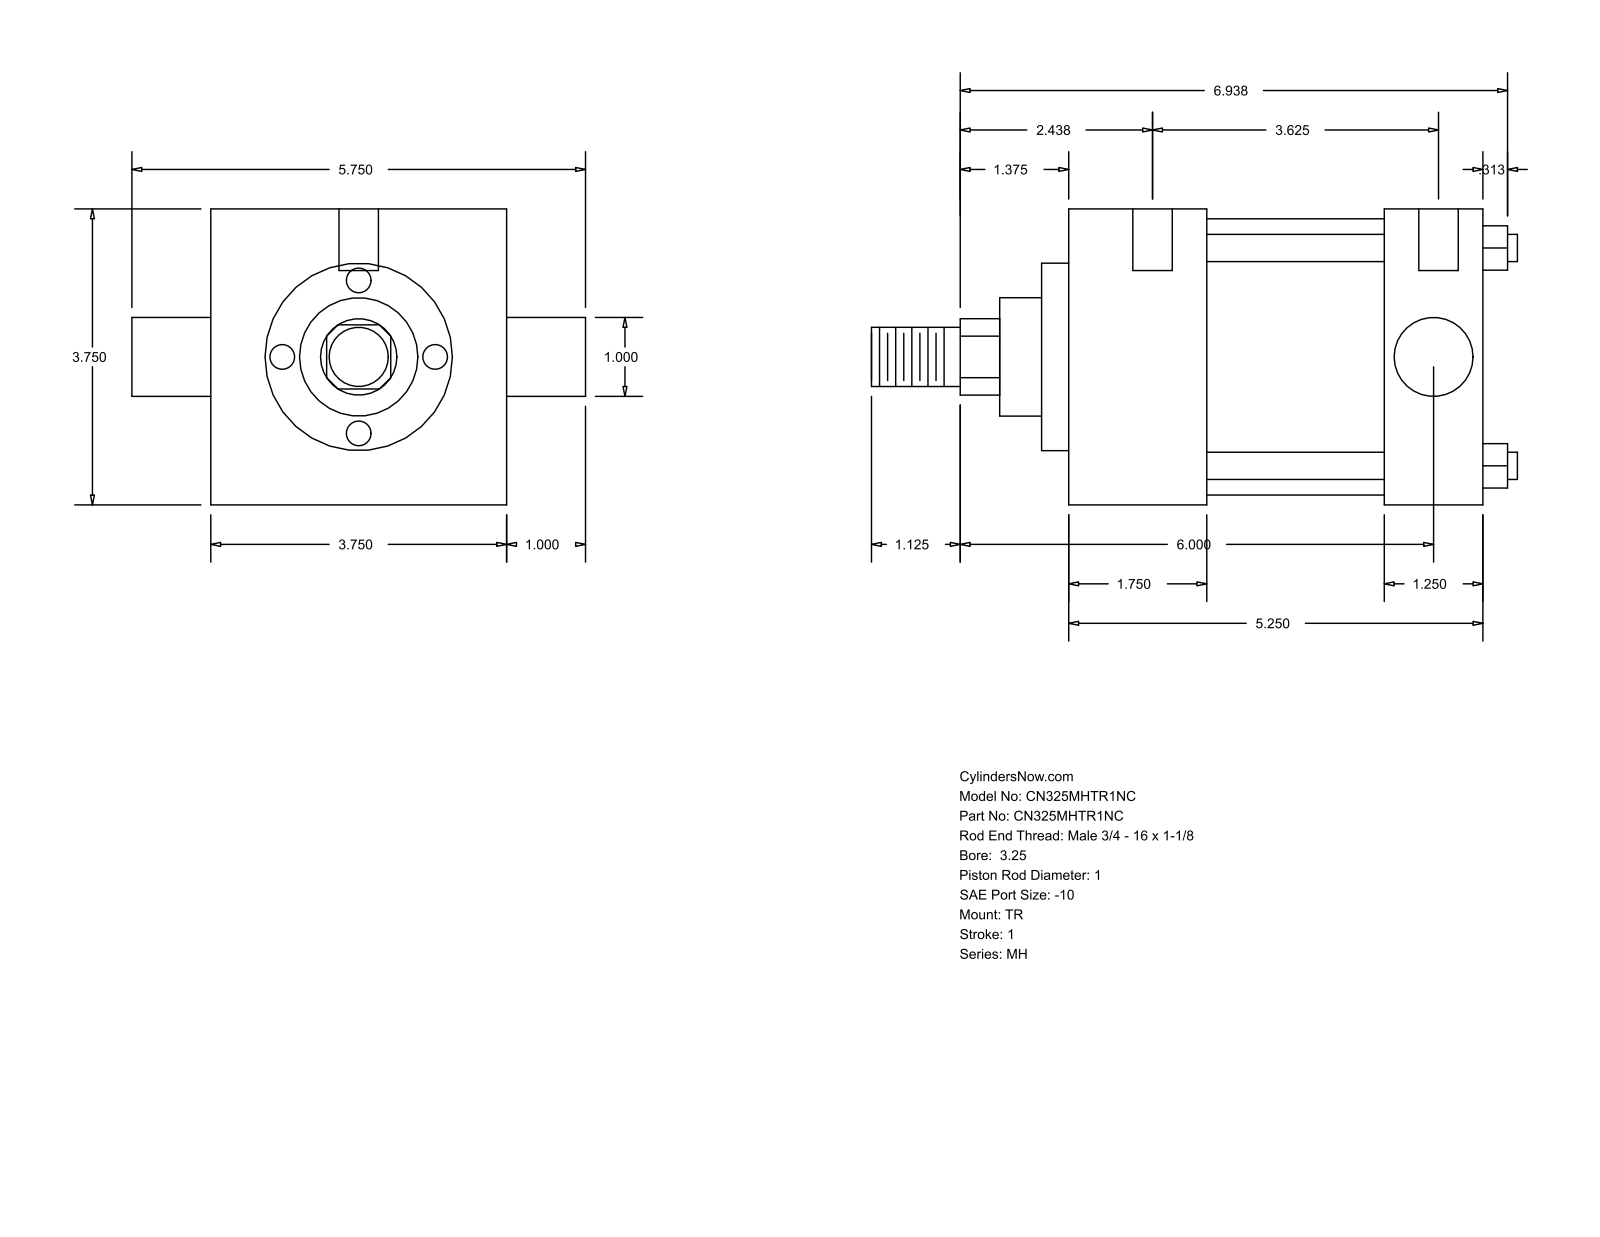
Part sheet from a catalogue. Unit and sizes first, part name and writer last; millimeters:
Units: millimetres
Overall size (bounding box): 207.96 × 146.05 × 95.25
Round holes (diameter × count): ⌀5.56 ×3, ⌀12.7 ×2
Round bosses / shafts (diameter × count): ⌀8.76 ×4, ⌀25.4 ×2, ⌀88.9 ×1, ⌀60.33 ×1, ⌀38.1 ×1, ⌀19.05 ×1
Partial cylindrical surfaces — rounded edges, fillets, slot ends (radius × count): R12.29 ×1
Main face-to-face distances: 95.24, 133.36, 44.46, 101.61, 57.15, 88.9, 31.75, 8.73, 53.19, 110.34
Hole centre spacings: 1.58, 4.76, 92.08, 93.66, 96.84, 98.42
Bodies: 0 solids, 86 faces (61 planar, 25 cylindrical, 0 other)
Part name (STEP PRODUCT): MH_TR__0325_1
STEP written by: GSSL Pune (CONFIG_CONTROL_DESIGN)
